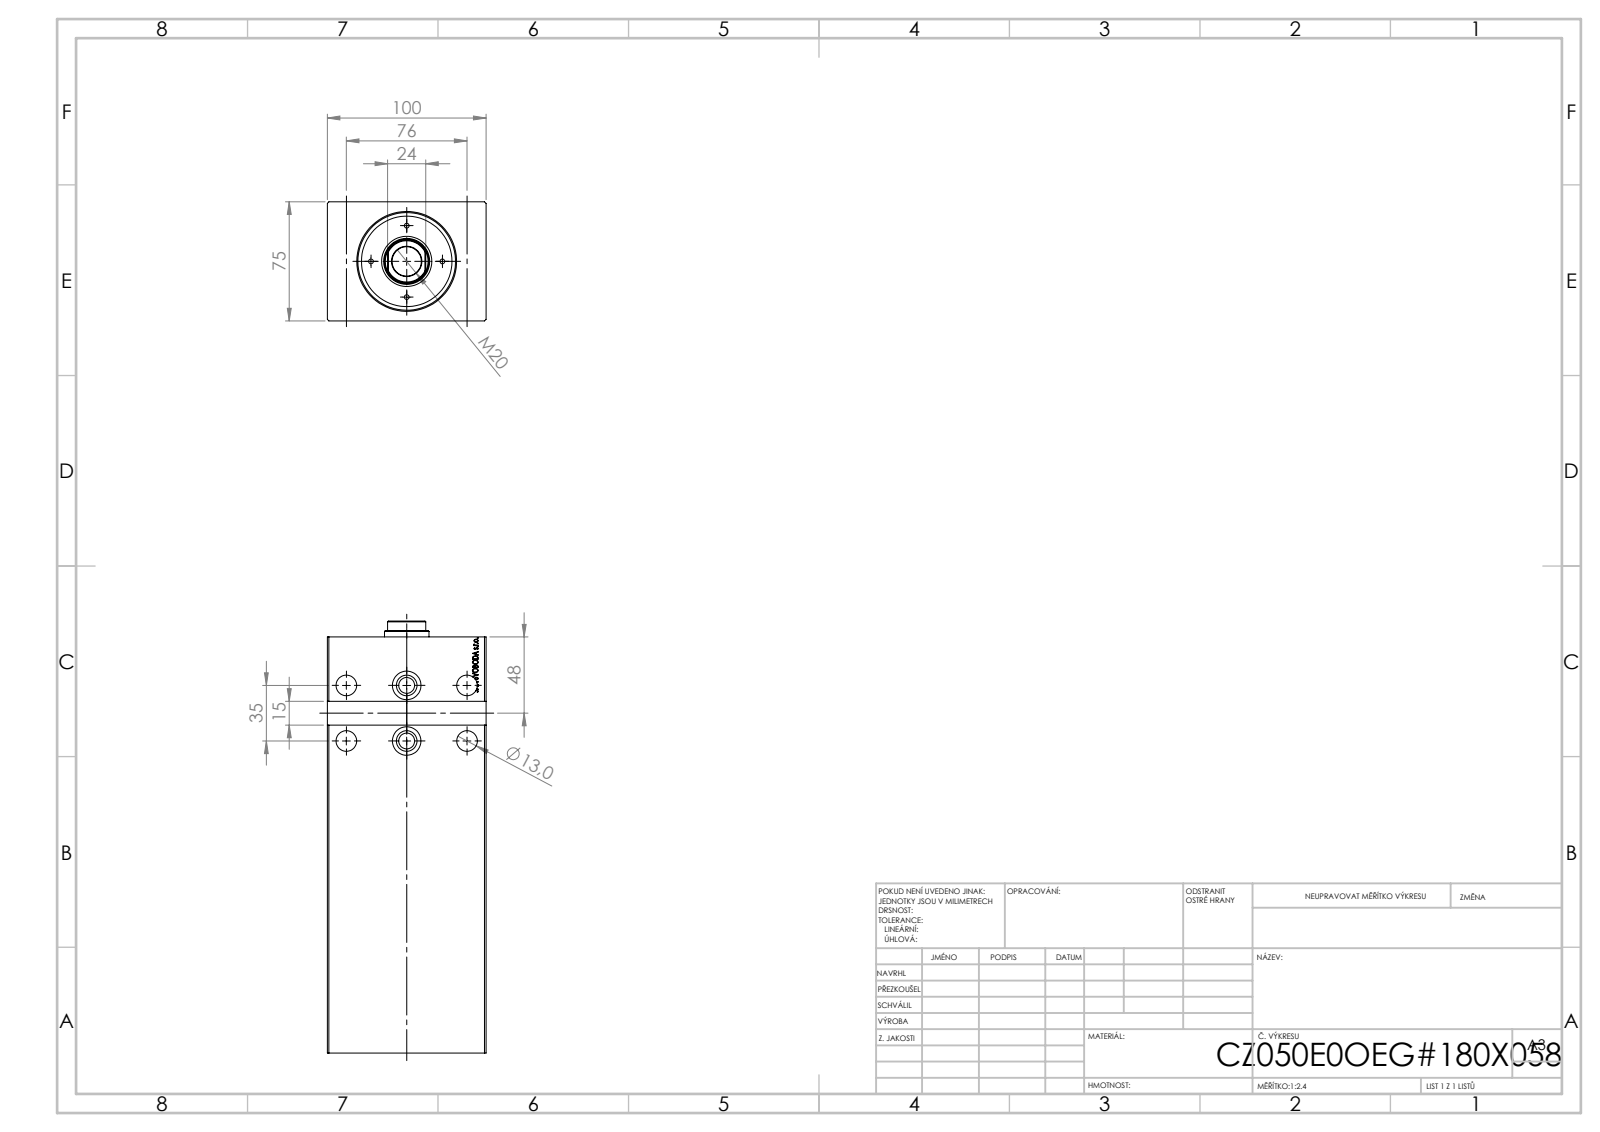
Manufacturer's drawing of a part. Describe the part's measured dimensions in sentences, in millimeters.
Its 3-D file was written by "SolidWorks 2019 (CONFIG_CONTROL_DESIGN)". It is 1 solid with 775 faces: 375 planar, 30 cylindrical and 370 other. Overall it measures 262 by 100 by 75 millimeters. Its volume is 1 431 000 cubic millimeters and its surface area 157 025 square millimeters. Round holes: 4 of diameter 13, 2 of diameter 8, 2 of diameter 10, 2 of diameter 18, 1 of diameter 36, 1 of diameter 50, 1 of diameter 61.5. Round bosses or shafts: 2 of diameter 13. The main face-to-face distances are 75, 100, 262, 244.2, 17.8, 2, 73, 261.8, 17.6, 10. The hole center spacings are 38, 51.66, 35, 76, 83.67, 19.14, 21.03, 33.71.
